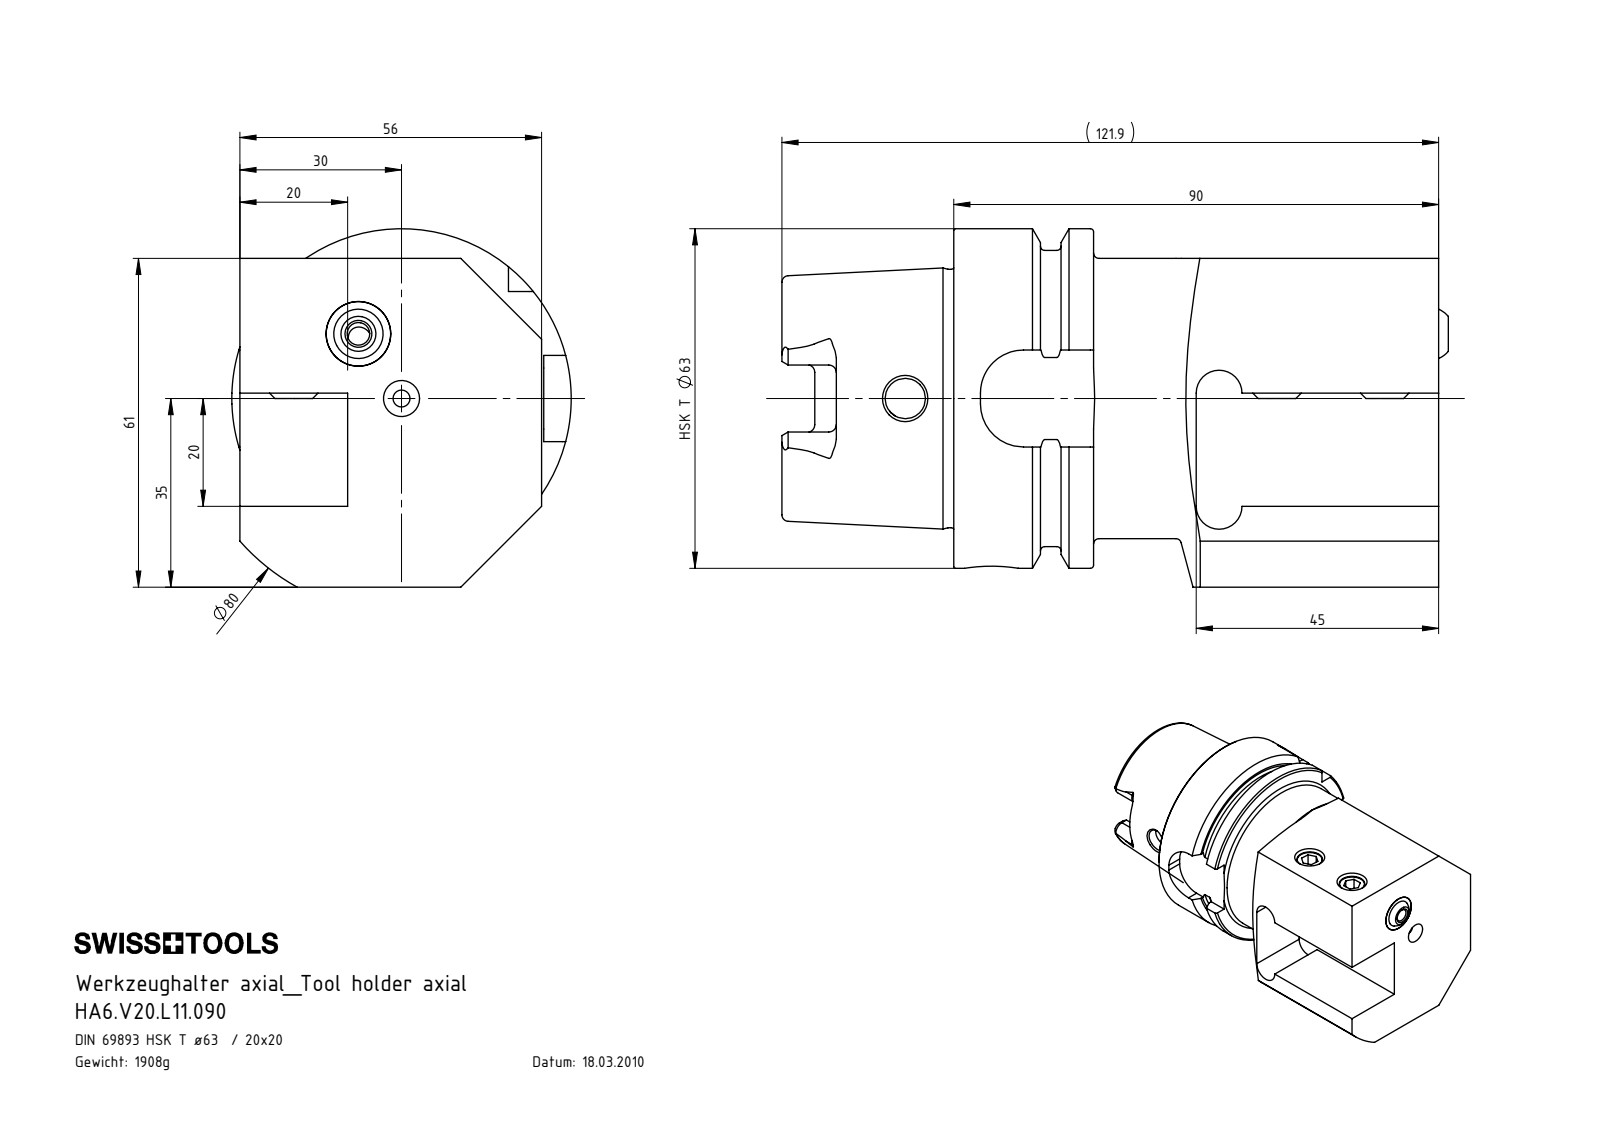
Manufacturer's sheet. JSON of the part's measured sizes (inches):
{"part_name": "KU1-U12.001.010; KU1-U12.001.010_2; KU1-U12.001.010_1; ISO 4026 - M10 x 25_Default (+2 more)", "step_written_by": "SolidWorks 2011 (AUTOMOTIVE_DESIGN)", "units": "inches", "bodies": {"solids": 5, "faces": 237, "planar": 75, "cylindrical": 68, "other": 94}, "overall_size": [4.913, 2.618, 2.48], "volume_in3": 14.85, "surface_area_in2": 68.88, "round_holes": [[0.165, 2], [0.335, 2], [0.124, 1], [0.276, 1], [0.295, 1], [0.331, 1], [0.394, 1], [0.472, 1], [0.669, 1], [0.748, 1], [1.339, 1], [1.575, 1]], "round_bosses_or_shafts": [[0.394, 2], [2.48, 1], [2.163, 1], [2.047, 1], [1.887, 1]], "partial_cylinders_radius": [[0.055, 6], [0.113, 4], [0.315, 4], [0.167, 2], [1.575, 1]], "face_to_face_distances": [1.417, 2.205, 2.402, 0.787, 3.543, 1.772, 0.591, 1.811, 0.984, 0.63], "hole_center_spacings": [0.568, 0.787, 2.23, 2.98]}
